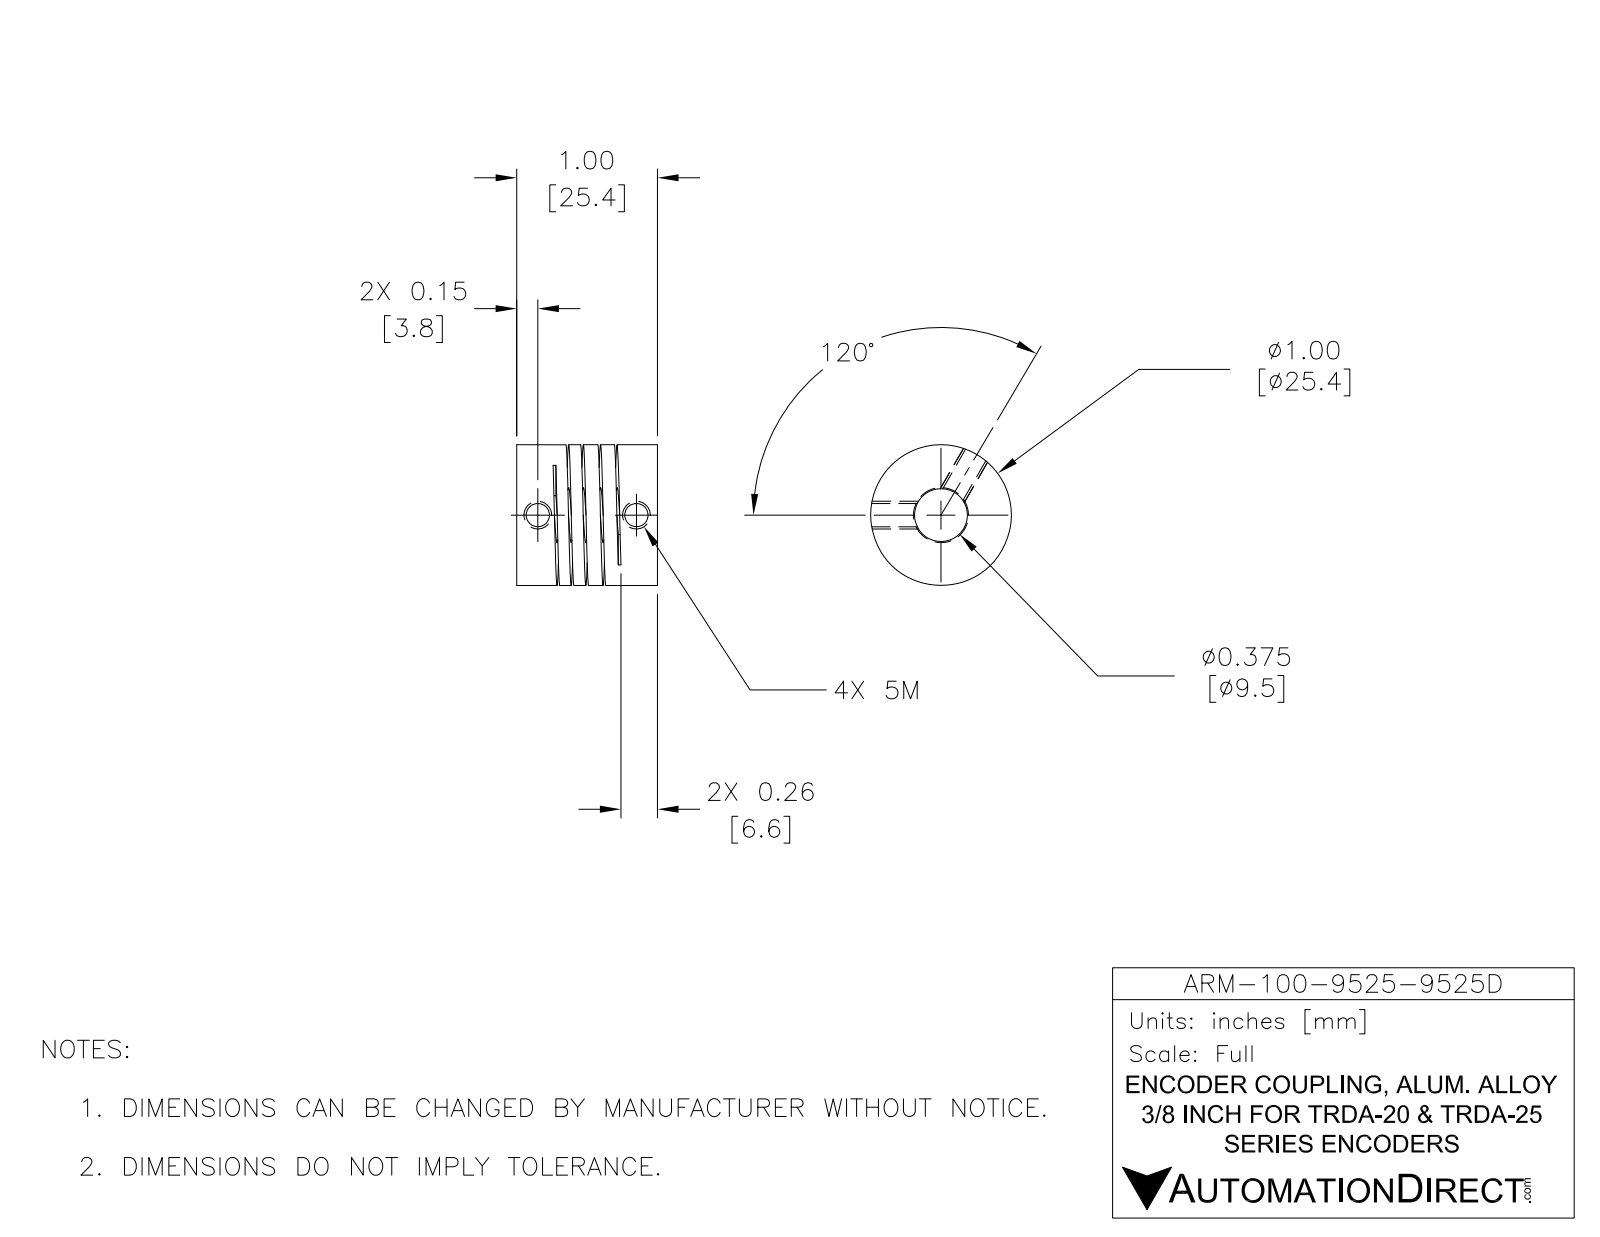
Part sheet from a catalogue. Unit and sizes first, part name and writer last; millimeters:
Units: millimetres
Overall size (bounding box): 25.4 × 25.4 × 25.4
Round holes (diameter × count): ⌀2.5 ×4, ⌀5 ×4, ⌀9.53 ×1, ⌀12 ×1
Round bosses / shafts (diameter × count): ⌀25.4 ×1
Main face-to-face distances: 25.4, 6.6, 18.8, 12.2, 15.36, 15.46, 15.47, 1.5
Hole centre spacings: 17.8
Volume: 9 456 mm³ · Surface area: 6 934 mm²
Bodies: 1 solid, 143 faces (58 planar, 46 cylindrical, 39 other)
Part name (STEP PRODUCT): ARM-100-9525-9525D
STEP written by: SolidWorks 2016 (AUTOMOTIVE_DESIGN)
